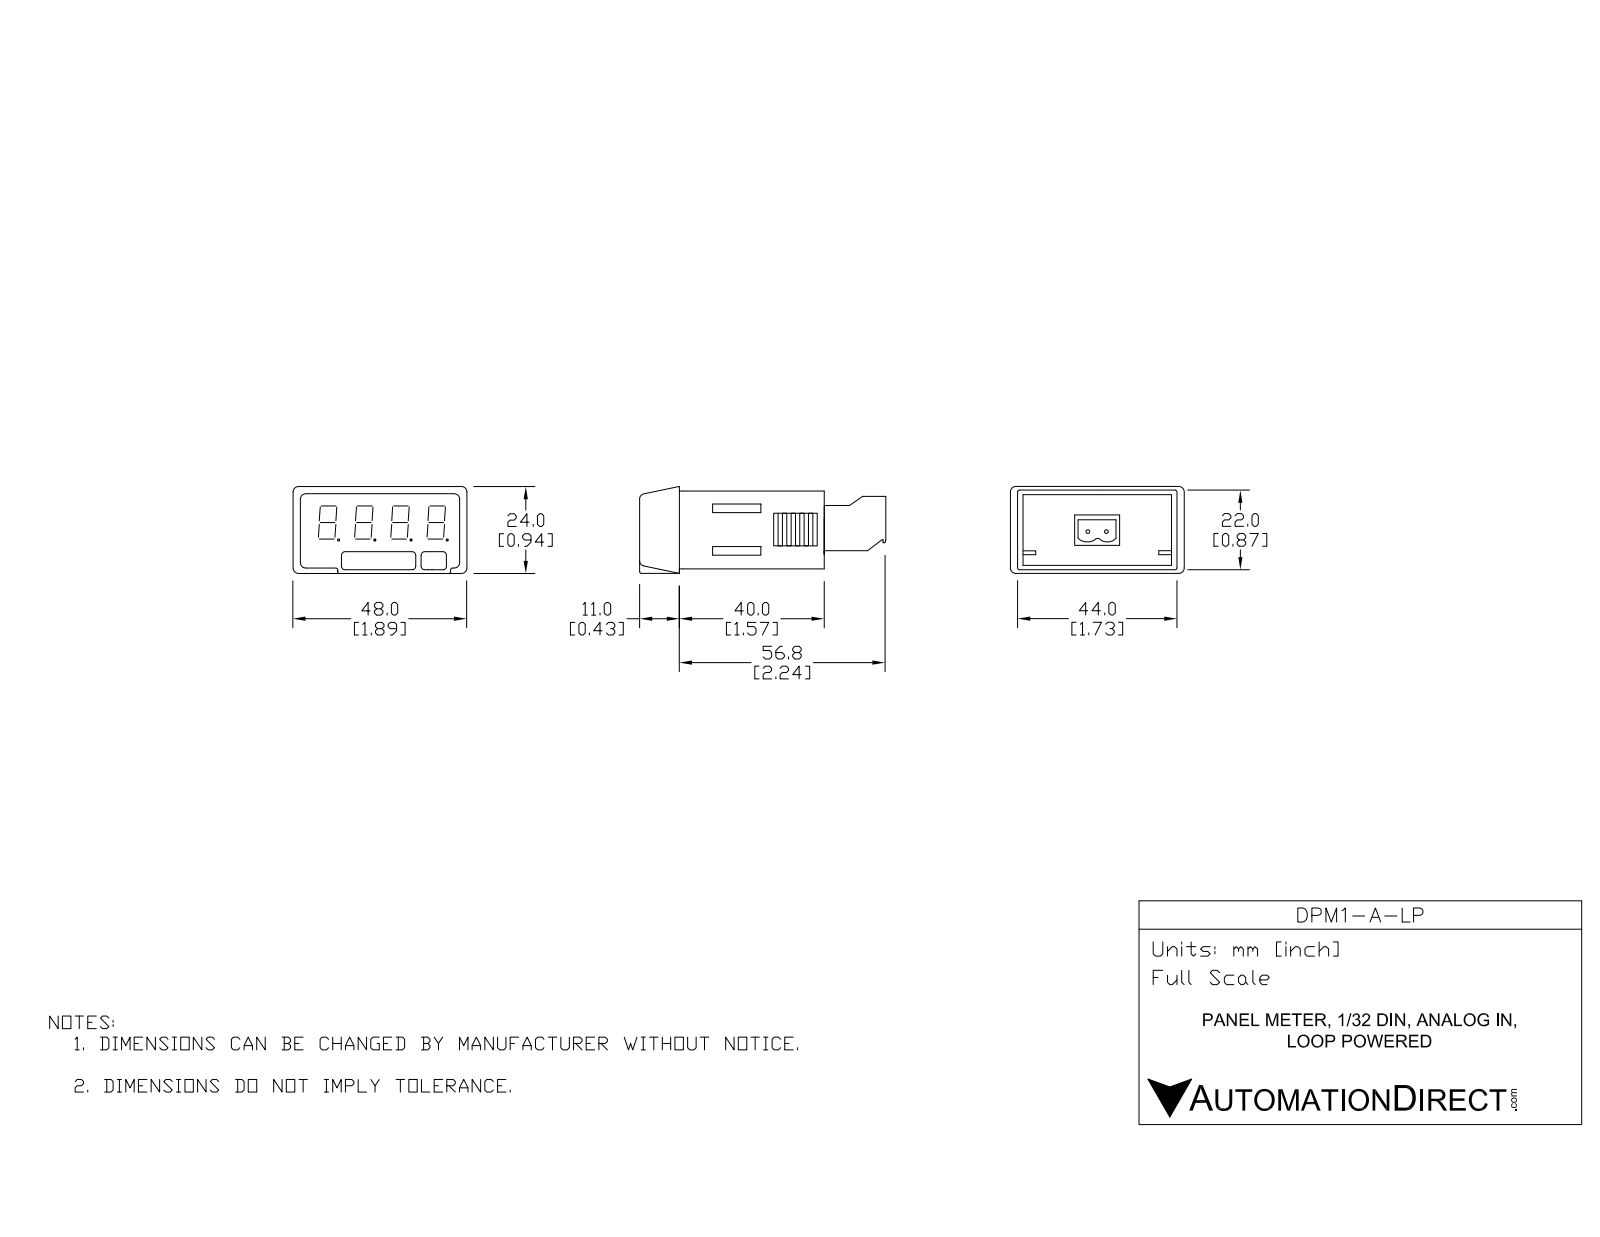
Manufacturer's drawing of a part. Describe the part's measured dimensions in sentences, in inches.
The part is named "DPM1-A-LP". Its 3-D file was written by "SolidWorks 2017 (AUTOMOTIVE_DESIGN)". It is 2 solids with 577 faces: 452 planar, 37 cylindrical and 88 other. Overall it measures 2.665 by 1.89 by 0.945 inches. Its volume is 1.315 cubic inches and its surface area 26.21 square inches. Round holes: 2 of diameter 0.078, 2 of diameter 0.118, 2 of diameter 0.152. Partial cylindrical surfaces (rounded edges, fillets, slot ends): 9 of radius 0.02, 4 of radius 0.039, 2 of radius 0.121, 1 of radius 0.025. The main face-to-face distances are 0.059, 0.807, 0.866, 0.748, 1.673, 2, 1.949, 0.051, 0.433, 1.516. The hole center spacings are 0.197, 0.201.
